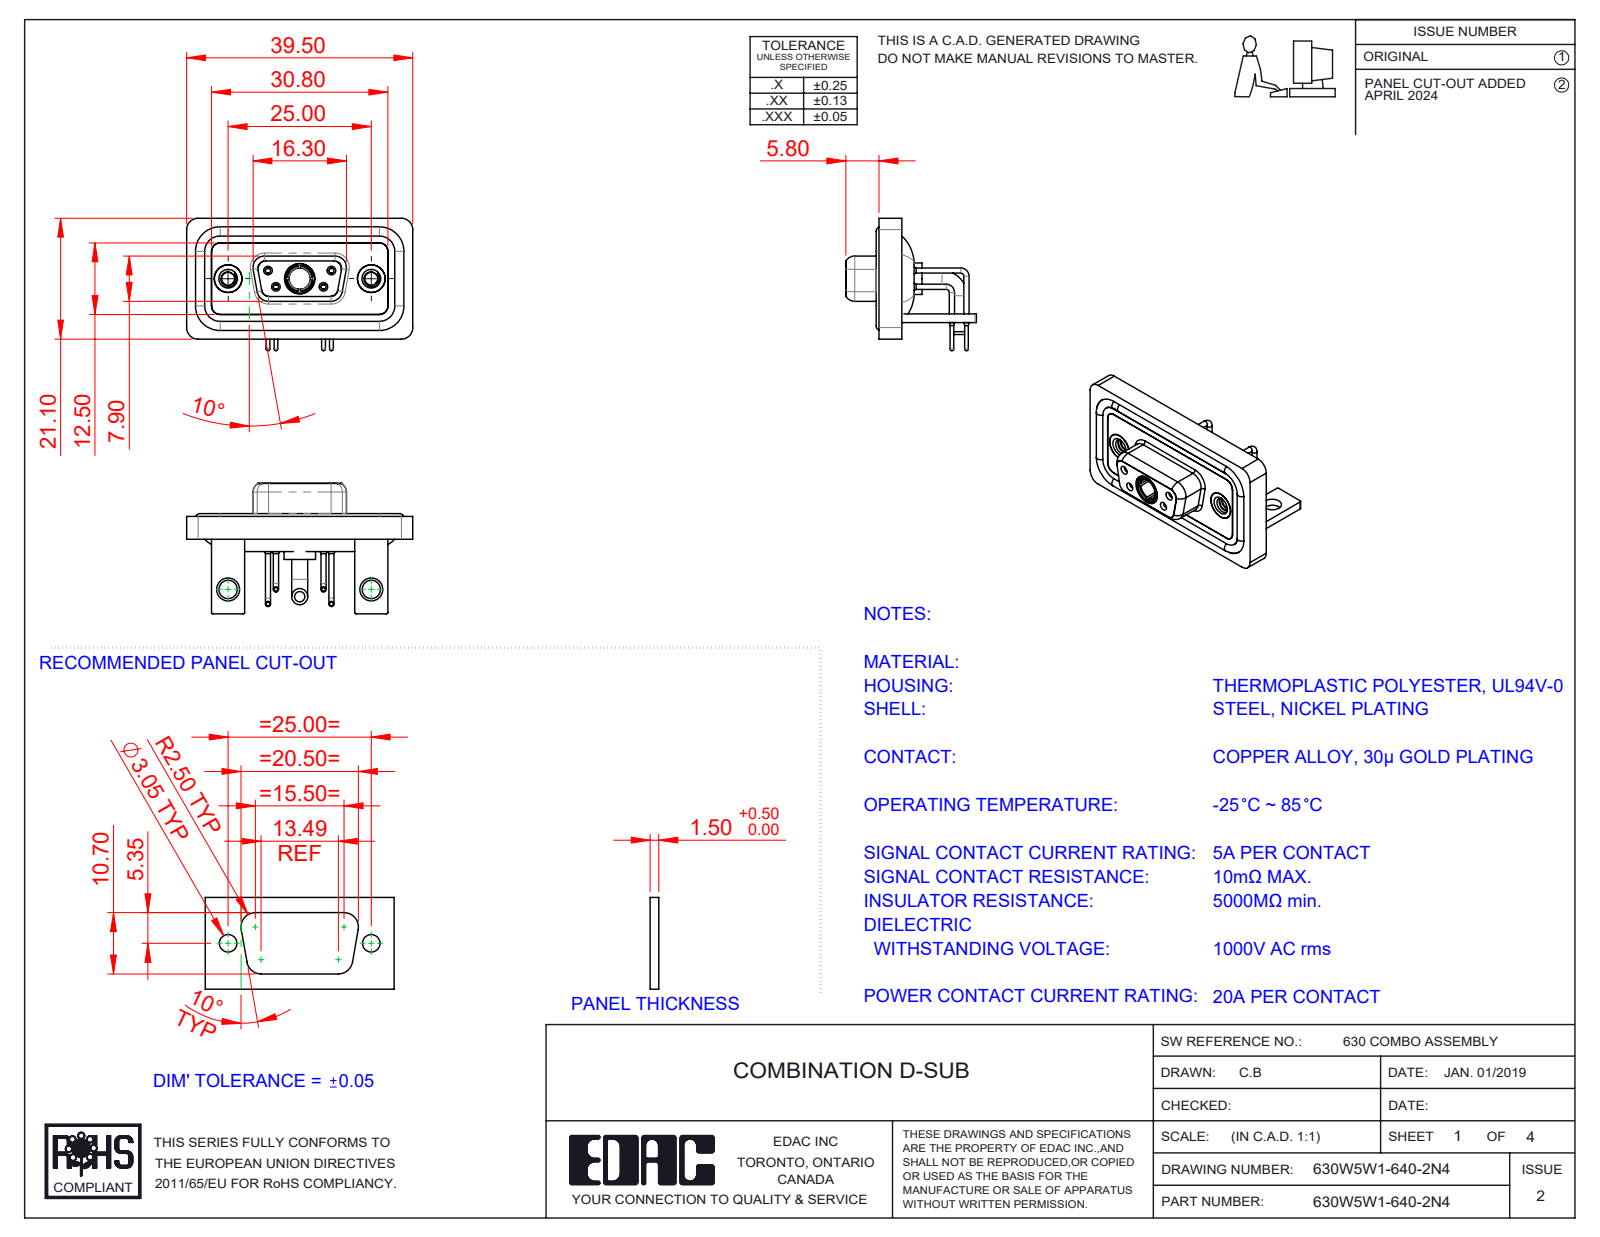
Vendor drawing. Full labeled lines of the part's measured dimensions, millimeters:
Part name (STEP PRODUCT): 630W5W1-640-2N4; 630Combo Stabilizer Bracket_50 Contacts; 630Combo Contact Row 2_50 Contacts; 630Combo Housing_5W1 (+6 more)
STEP written by: SolidWorks 2023 (CONFIG_CONTROL_DESIGN)
Units: millimetres
Bodies: 15 solids, 724 faces (214 planar, 329 cylindrical, 181 other)
Overall size (bounding box): 39.5 × 23.12 × 22.8
Volume: 5 195 mm³ · Surface area: 8 579 mm²
Round holes (diameter × count): ⌀0.9 ×4, ⌀1.1 ×4, ⌀1.5 ×4, ⌀2 ×4, ⌀4.85 ×3, ⌀1.6 ×2, ⌀1.7 ×2, ⌀2.26 ×2, ⌀3.2 ×2, ⌀4 ×2, ⌀4.05 ×2, ⌀5 ×2
Round bosses / shafts (diameter × count): ⌀1.6 ×6, ⌀0.9 ×4, ⌀0.65 ×4, ⌀4.95 ×2, ⌀4.8 ×2, ⌀2.8 ×2, ⌀5.5 ×1, ⌀5.2 ×1
Partial cylindrical surfaces — rounded edges, fillets, slot ends (radius × count): R2 ×19, R1.5 ×18, R0.25 ×16, R1.35 ×8, R1.6 ×8, R0.5 ×5, R0.6 ×4, R0.65 ×4
Main face-to-face distances: 0.4, 2.9, 1.5, 1.8, 1.1, 3.7, 1.6, 0.8, 2.5, 3.1
Hole centre spacings: 3.16, 5.72, 7.1, 12.5, 18.1, 25, 4.39, 4.4
